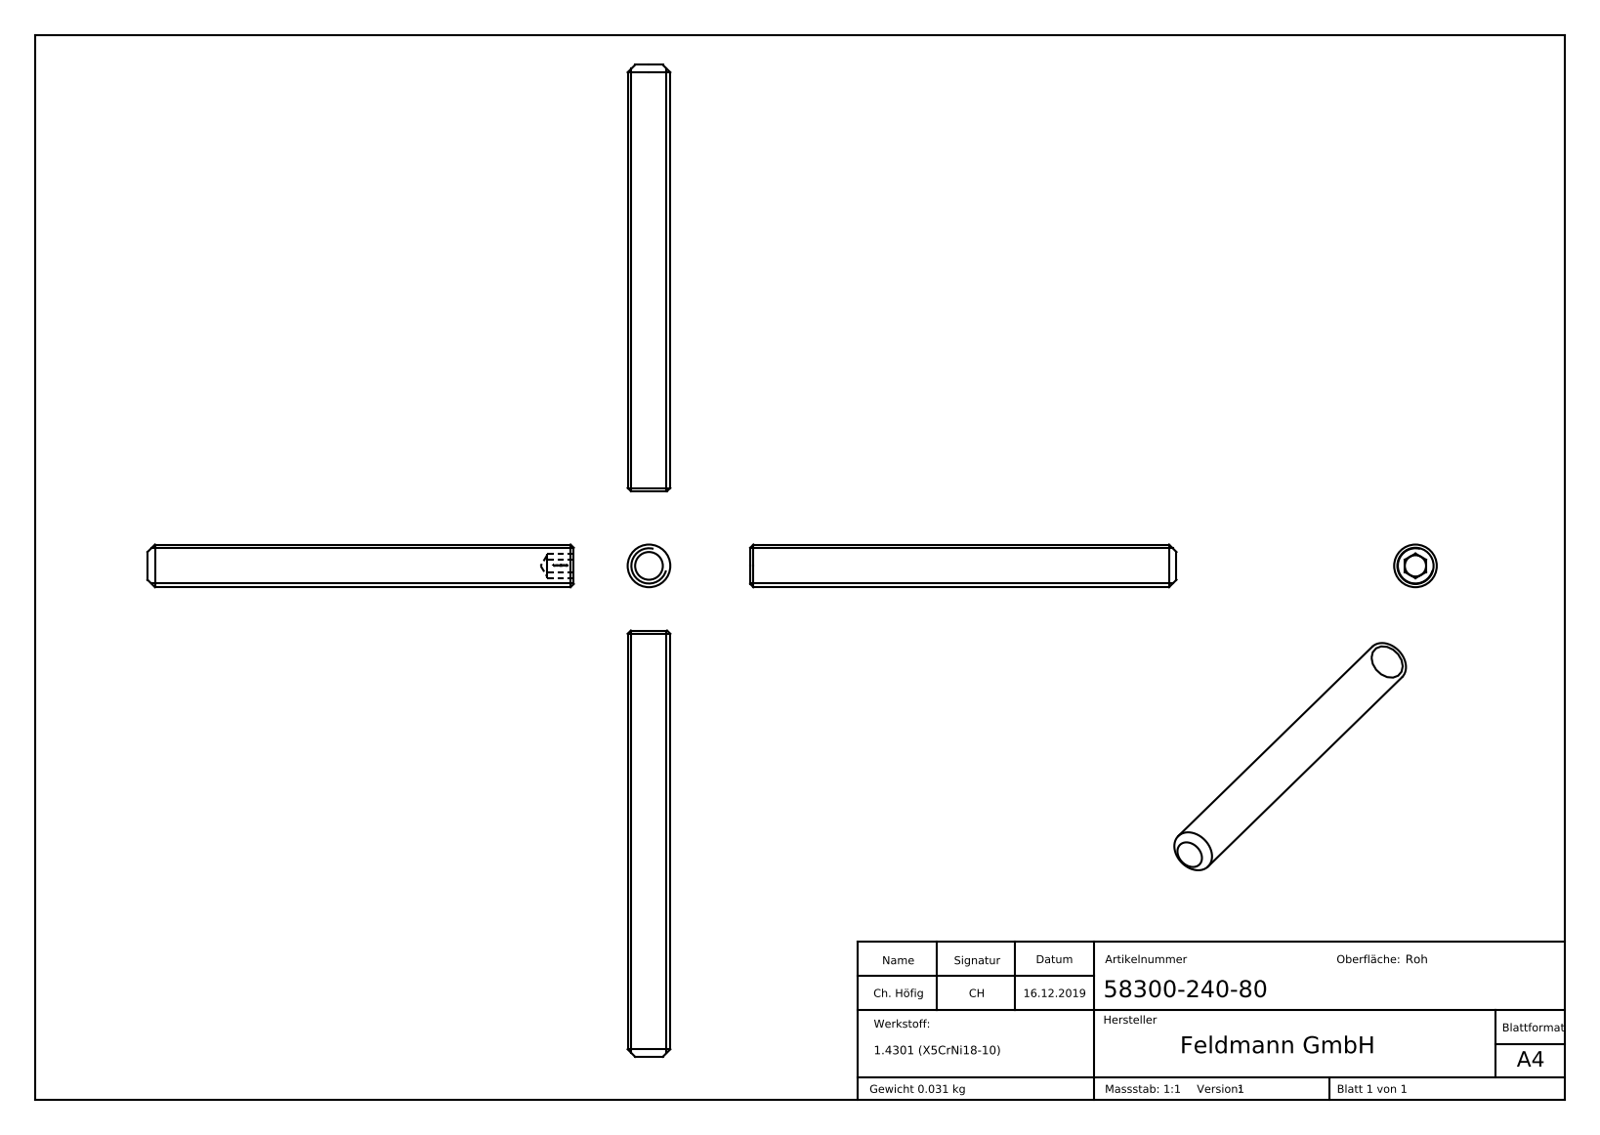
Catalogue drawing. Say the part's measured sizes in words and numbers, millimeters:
The part is named "58300-240-80". Its 3-D file was written by "SolidWorks 2015 (CONFIG_CONTROL_DESIGN)". It is 1 solid with 298 faces: 135 planar, 1 cylindrical and 162 other. Overall it measures 82 by 8 by 8 millimeters. Its volume is 3 921 cubic millimeters and its surface area 2 152 square millimeters. Round bosses or shafts: 1 of diameter 8. The main face-to-face distances are 4, 80, 75, 5, 4.1, 0.48, 0.54, 1.67, 0.31, 1.6.
